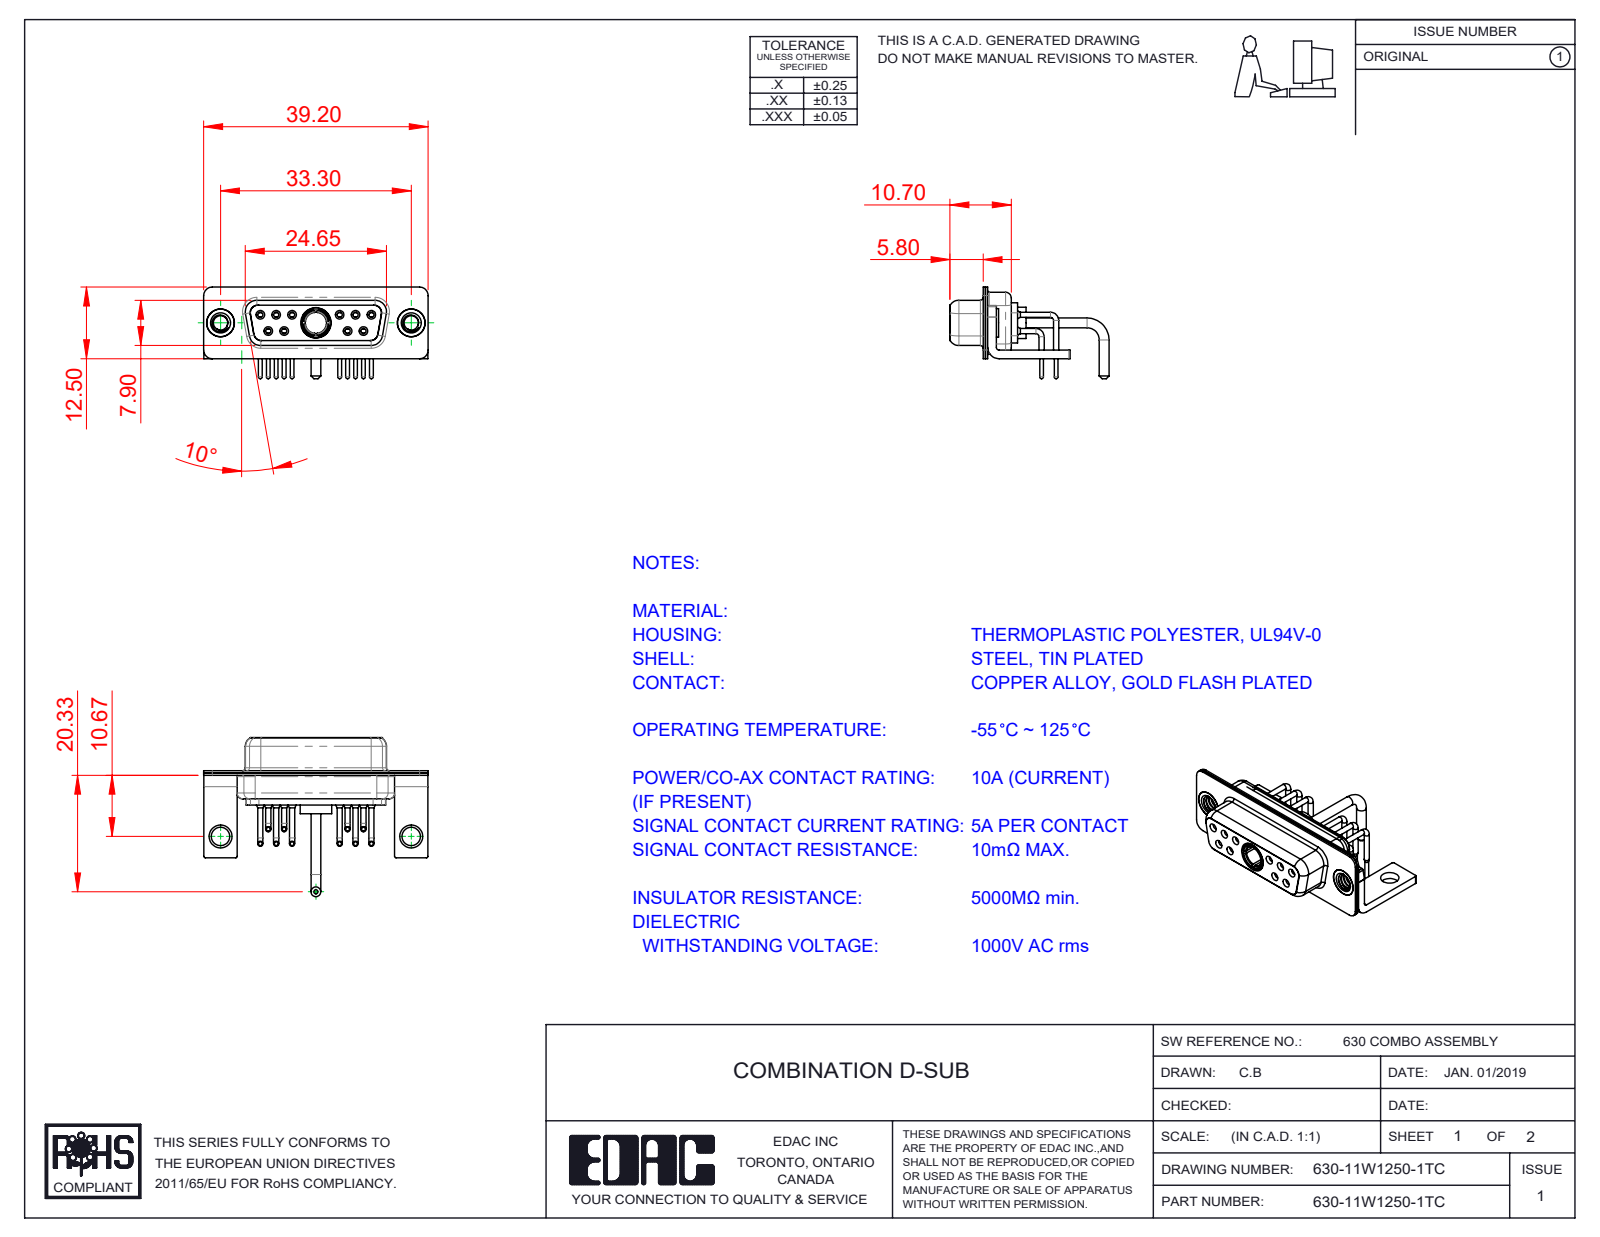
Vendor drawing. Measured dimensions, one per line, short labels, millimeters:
name: 630-11W1250-1TC; 630Combo Shell Rear_15 Contacts; 630Combo Shell Front_15 Contacts; 630Combo Stabilizer Bracket (+5 more)
written by: SolidWorks 2020 (CONFIG_CONTROL_DESIGN)
unit: mm
bodies: 19 solids, 925 faces (266 planar, 410 cylindrical, 249 other)
size: 39.2 × 27.78 × 16
volume: 2 866 mm³; area: 6 847 mm²
holes: 10× ⌀0.9, 10× ⌀1.1, 10× ⌀1.5, 10× ⌀2, 6× ⌀1.7, 4× ⌀1.6, 3× ⌀4.85, 2× ⌀2.5, 2× ⌀3.2, 2× ⌀4, 2× ⌀4.05, 1× ⌀3.7
bosses: 10× ⌀0.9, 10× ⌀0.65, 6× ⌀1.6, 2× ⌀5, 2× ⌀4.95, 2× ⌀4.8, 2× ⌀1.7, 1× ⌀5.5
rounds: 16× R0.25, 16× R1.5, 13× R2, 12× R1.35, 8× R1.6, 5× R0.5, 4× R0.6, 4× R0.65
face distances: 0.4, 0.8, 1.4, 0.45, 8.45, 1.5, 1.8, 8.9, 6.2, 2.3
hole spacings: 3.16, 2.77, 13.85, 11.08, 16.62, 5.03, 5.04, 5.54
